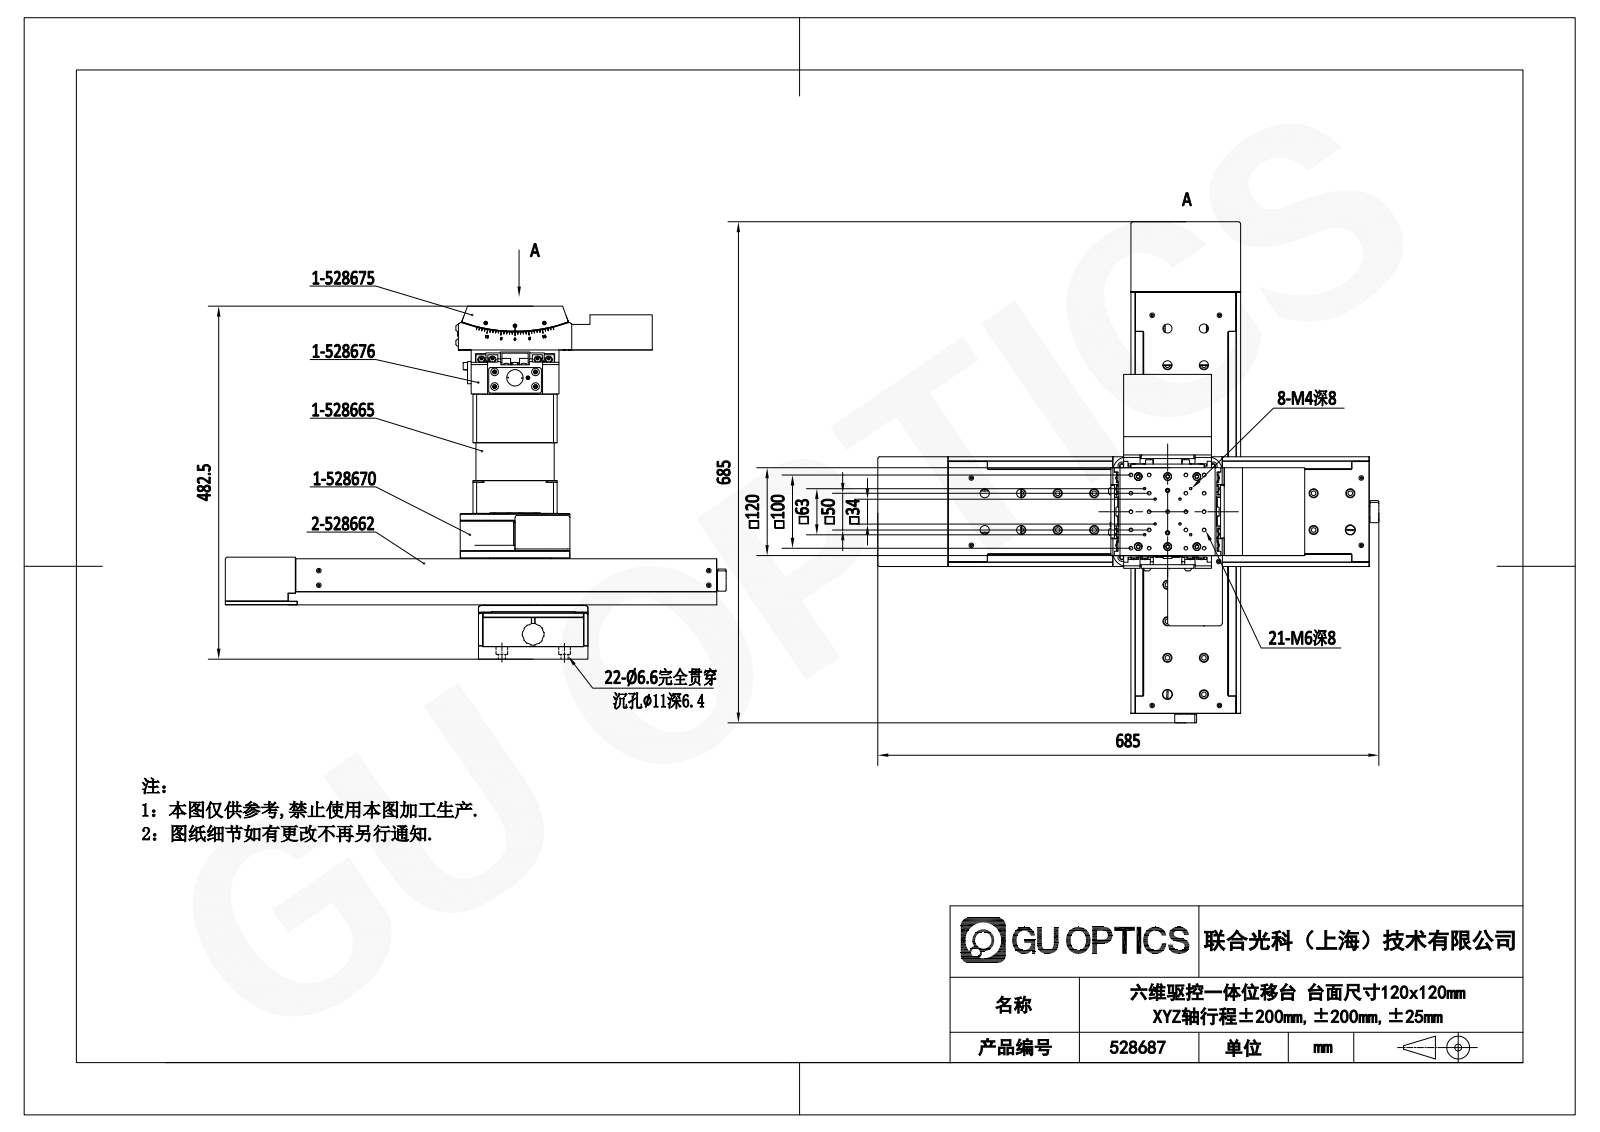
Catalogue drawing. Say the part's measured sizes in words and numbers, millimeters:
The part is named "528675; 528665; 528663; 528687 (+2 more)". Its 3-D file was written by "SolidWorks 2020 (CONFIG_CONTROL_DESIGN)". It is 263 solids with 10632 faces: 6569 planar, 2328 cylindrical and 1735 other. Overall it measures 685 by 685 by 482.5 millimeters. Its volume is 10 750 000 cubic millimeters and its surface area 2 936 000 square millimeters. Round holes: 192 of diameter 5, 115 of diameter 3.3, 87 of diameter 11, 82 of diameter 3.4, 80 of diameter 2.5, 77 of diameter 6.5, 67 of diameter 6.6, 48 of diameter 8, 44 of diameter 12.5, 32 of diameter 2.46, 32 of diameter 3.5, 29 of diameter 6. Round bosses or shafts: 44 of diameter 4, 35 of diameter 6, 32 of diameter 10, 24 of diameter 7, 8 of diameter 9.5, 8 of diameter 8.5, 8 of diameter 2.5, 7 of diameter 5. Partial cylindrical surfaces (rounded edges, fillets, slot ends): 93 of radius 5, 59 of radius 2, 45 of radius 1, 36 of radius 0.3, 20 of radius 3.5, 19 of radius 3, 18 of radius 7.5, 10 of radius 4. The main face-to-face distances are 74, 6, 57, 63, 45, 18, 39, 17, 144, 131. The hole center spacings are 12.5, 62.5, 25, 37.5, 50, 27.95, 39.53, 51.54.
